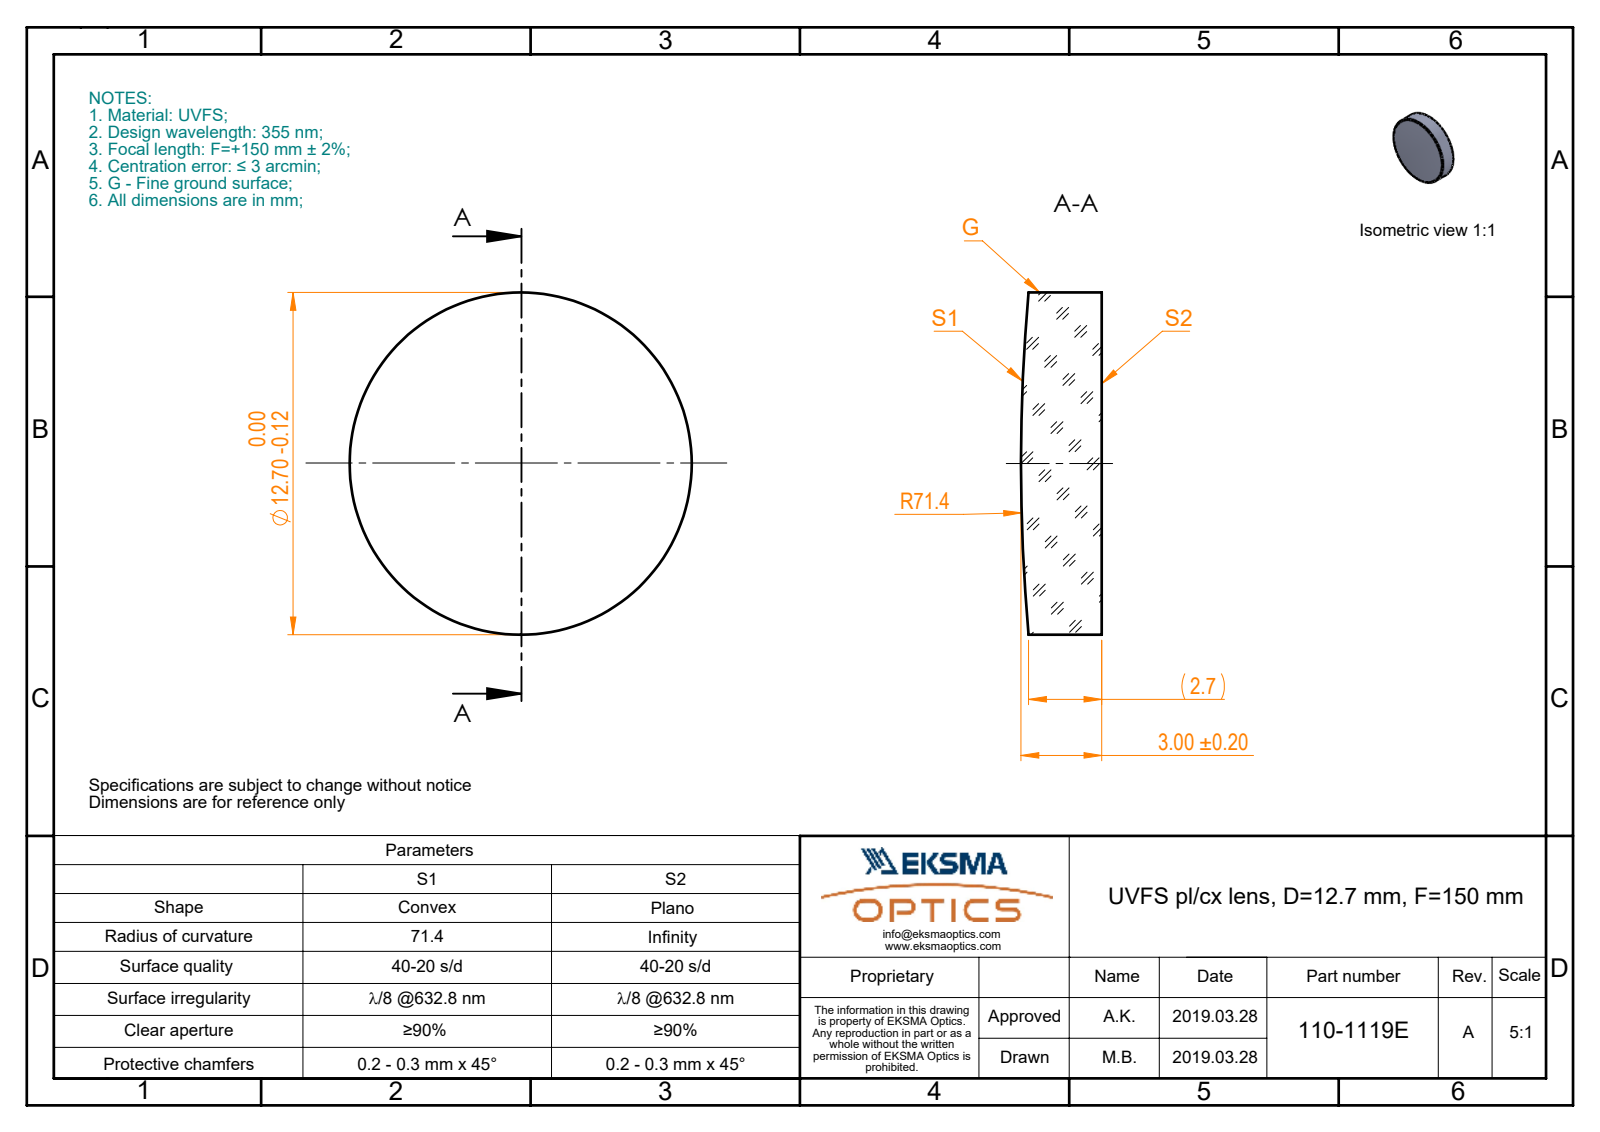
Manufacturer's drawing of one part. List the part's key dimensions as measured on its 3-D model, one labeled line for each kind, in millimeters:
Part name (STEP PRODUCT): 110-1119E UVFS pl-cx 12.7 F150
STEP written by: SolidWorks 2017 (CONFIG_CONTROL_DESIGN)
Units: millimetres
Bodies: 1 solid, 5 faces (1 planar, 2 cylindrical, 2 other)
Overall size (bounding box): 12.7 × 12.7 × 3
Volume: 362 mm³ · Surface area: 362 mm²
Round bosses / shafts (diameter × count): ⌀12.7 ×1
